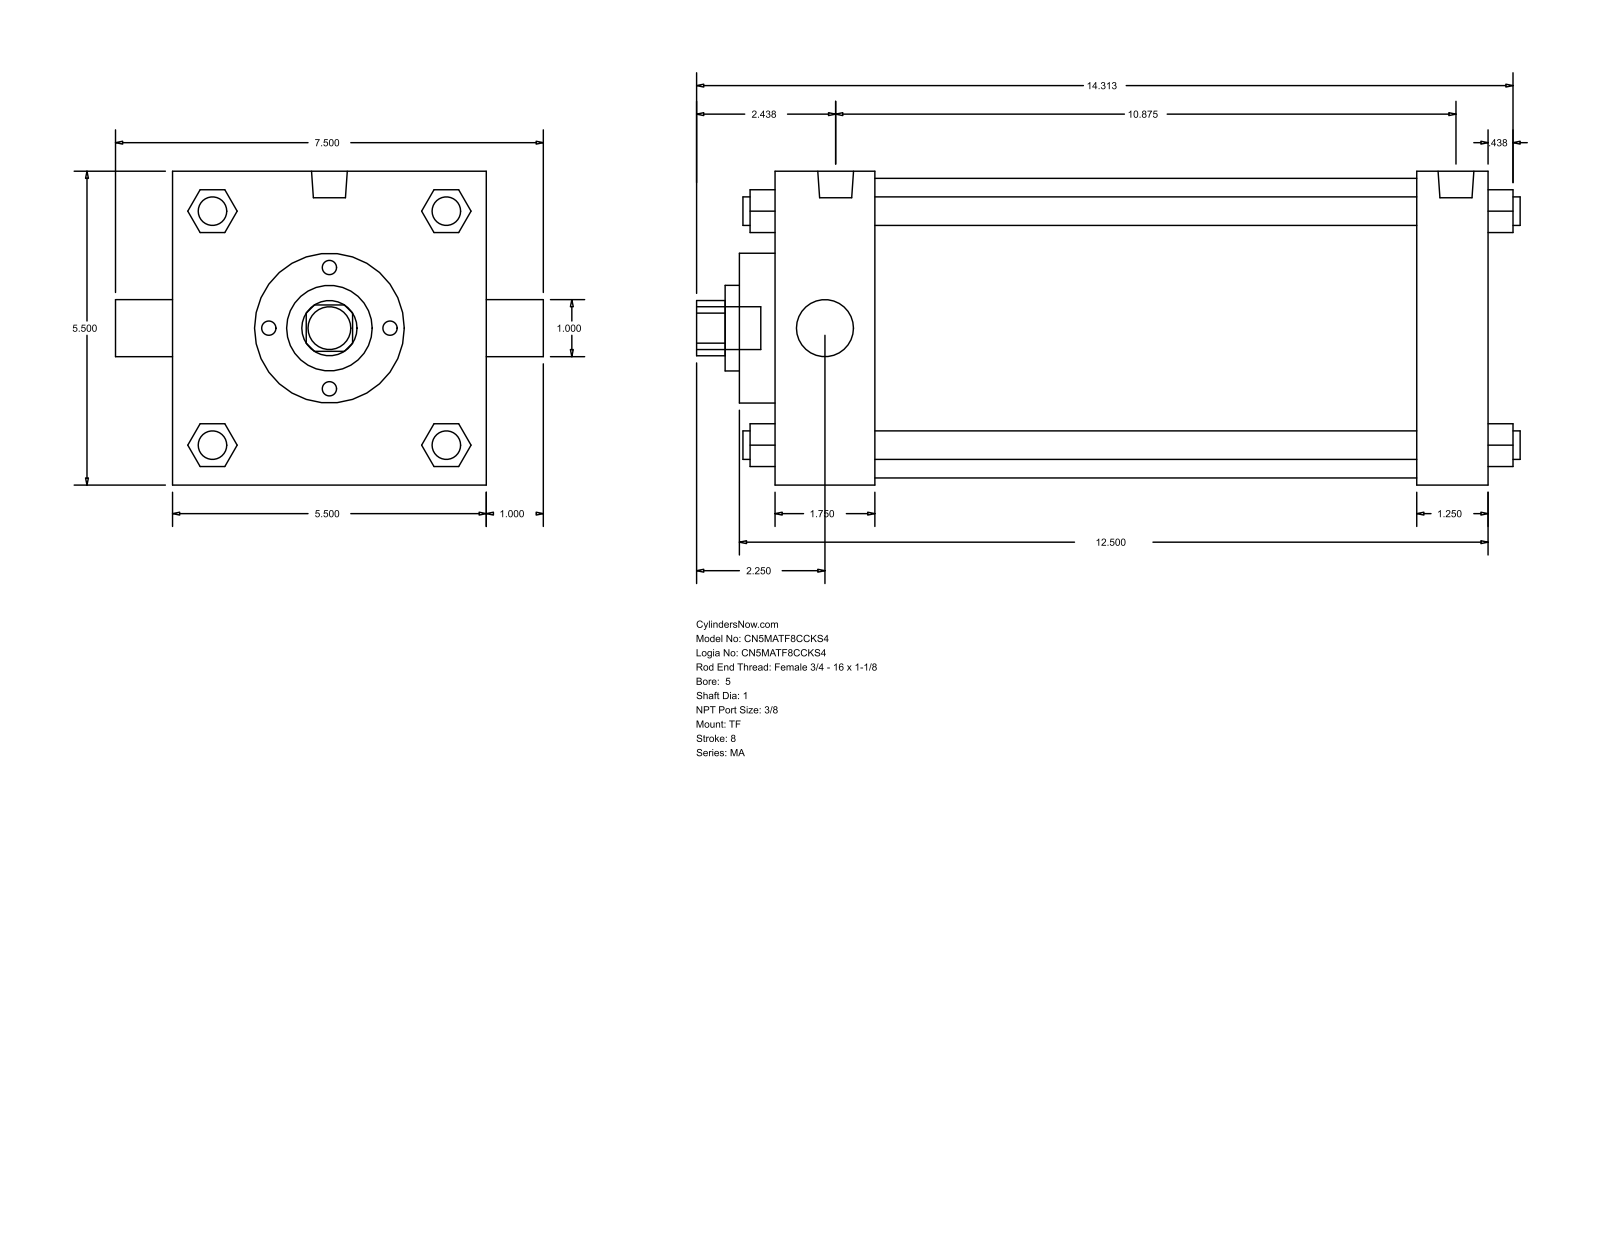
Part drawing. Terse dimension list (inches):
name: MA_TF__0500_1
written by: GSSL Pune (CONFIG_CONTROL_DESIGN)
unit: in
bodies: 0 solids, 122 faces (93 planar, 29 cylindrical, 0 other)
size: 14.437 × 7.5 × 5.5
holes: 2× ⌀1, 1× ⌀1.5, 1× ⌀2.625, 1× ⌀5.25
bosses: 4× ⌀0.5, 3× ⌀0.437, 2× ⌀0.627, 1× ⌀0.75
rounds: 1× R0.484
face distances: 5.5, 12.5, 11.25, 1.25, 1.75, 9.5, 10.75, 0.625, 2.375, 11.875
